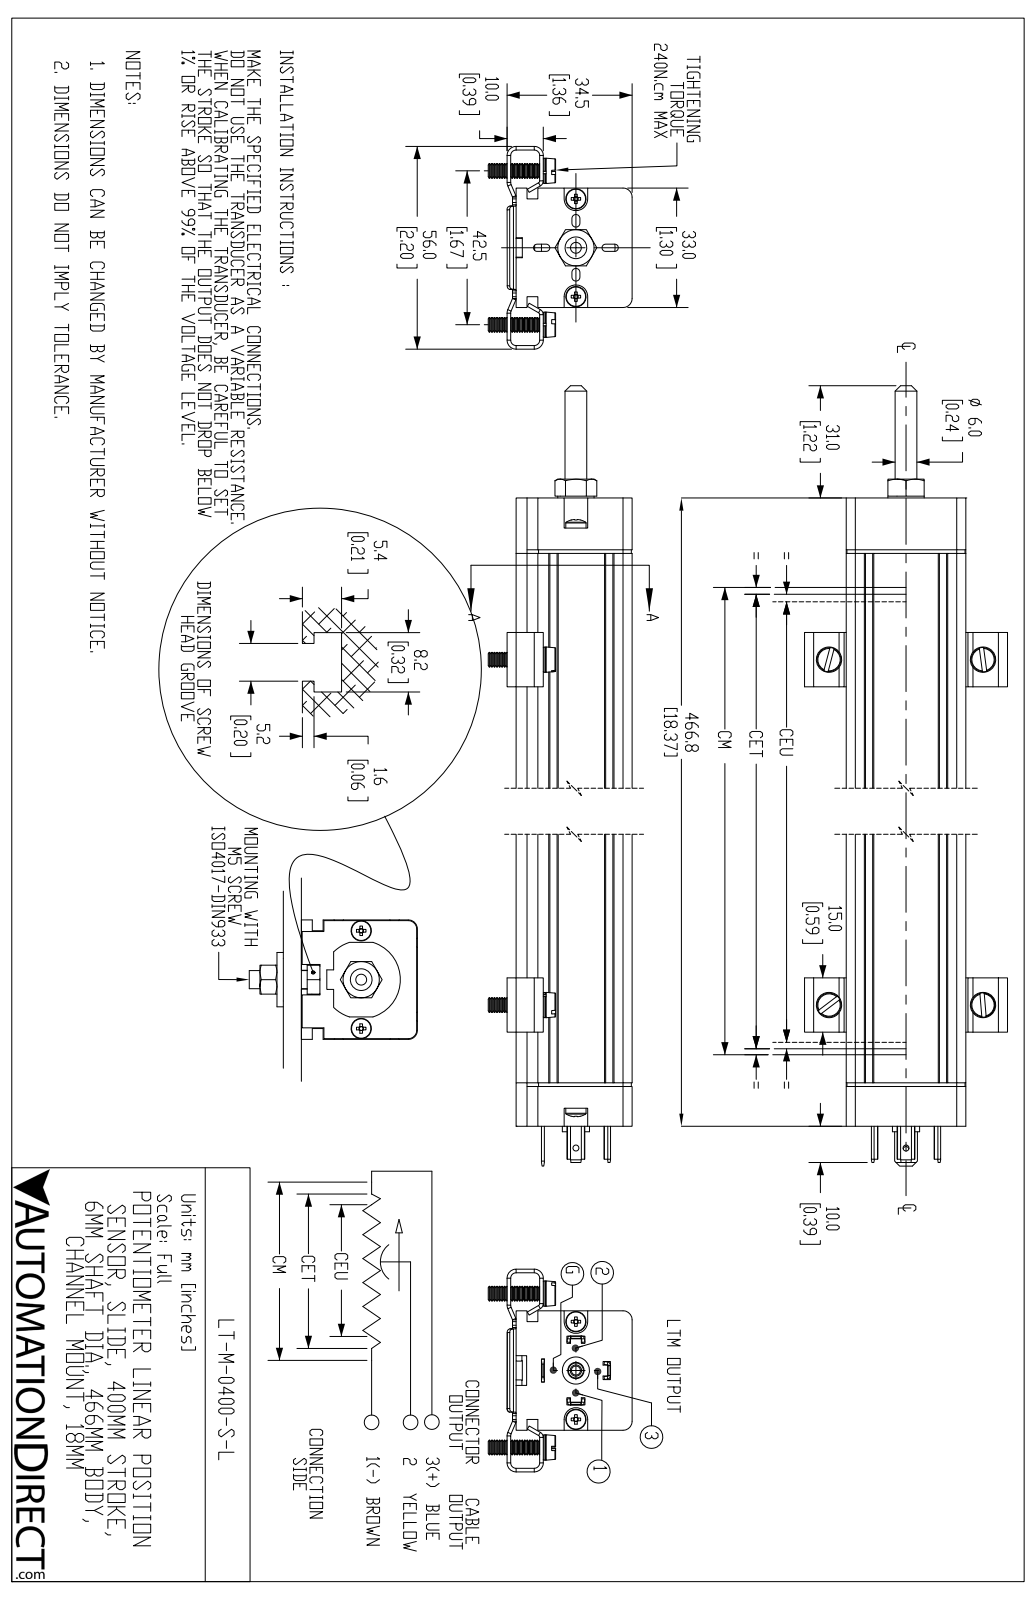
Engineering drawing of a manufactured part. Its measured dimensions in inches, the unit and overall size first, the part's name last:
Units: inches
Overall size (bounding box): 20.725 × 2.205 × 1.563
Round holes (diameter × count): ⌀0.142 ×4, ⌀0.059 ×2, ⌀0.065 ×2, ⌀0.108 ×2, ⌀0.134 ×2, ⌀0.169 ×2, ⌀0.063 ×1, ⌀0.098 ×1, ⌀0.118 ×1, ⌀0.163 ×1, ⌀0.197 ×1, ⌀0.276 ×1
Round bosses / shafts (diameter × count): ⌀0.274 ×4, ⌀0.157 ×4, ⌀0.22 ×2, ⌀0.118 ×2, ⌀0.295 ×1, ⌀0.236 ×1, ⌀0.177 ×1, ⌀0.173 ×1
Partial cylindrical surfaces — rounded edges, fillets, slot ends (radius × count): R0.039 ×34, R0.098 ×12, R0.059 ×10, R0.085 ×8, R0.033 ×6, R0.043 ×4, R0.024 ×2, R0.063 ×2
Main face-to-face distances: 1.26, 1.299, 0.118, 1.287, 0.213, 1.047, 0.488, 0.799, 0.811, 0.476
Hole centre spacings: 0.484, 0.531, 1.359, 1.663, 1.673, 1.766, 1.78, 15.74
Volume: 28.9 in³ · Surface area: 164.7 in²
Bodies: 21 solids, 1620 faces (696 planar, 356 cylindrical, 568 other)
Part name (STEP PRODUCT): LT-M-0400-S-L
STEP written by: SolidWorks 2019 (AUTOMOTIVE_DESIGN)
